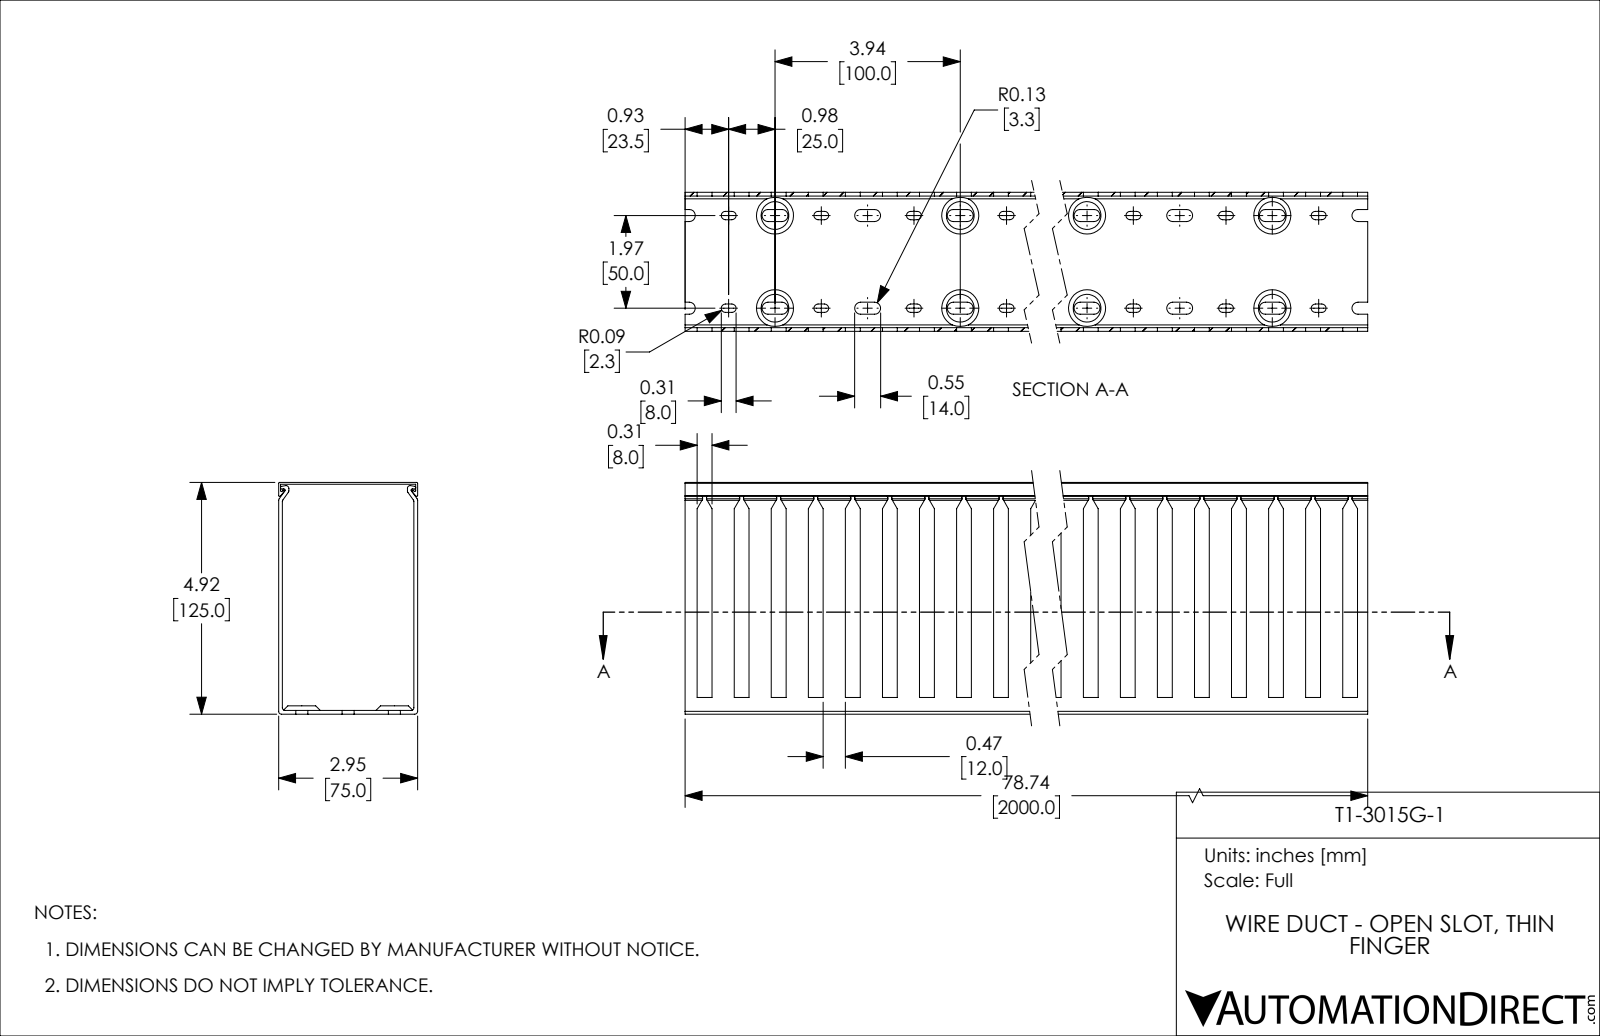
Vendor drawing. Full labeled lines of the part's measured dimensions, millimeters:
Part name (STEP PRODUCT): T1-3050W-1
STEP written by: SolidWorks 2021 (CONFIG_CONTROL_DESIGN)
Units: millimetres
Bodies: 2 solids, 1573 faces (762 planar, 731 cylindrical, 80 other)
Overall size (bounding box): 2000 × 125 × 75
Volume: 1 440 000 mm³ · Surface area: 1 633 000 mm²
Partial cylindrical surfaces — rounded edges, fillets, slot ends (radius × count): R3.25 ×200, R2.25 ×160, R1.5 ×12, R0.5 ×8, R0.75 ×6
Main face-to-face distances: 2, 73, 75, 71, 1, 124, 125, 122, 123, 72
